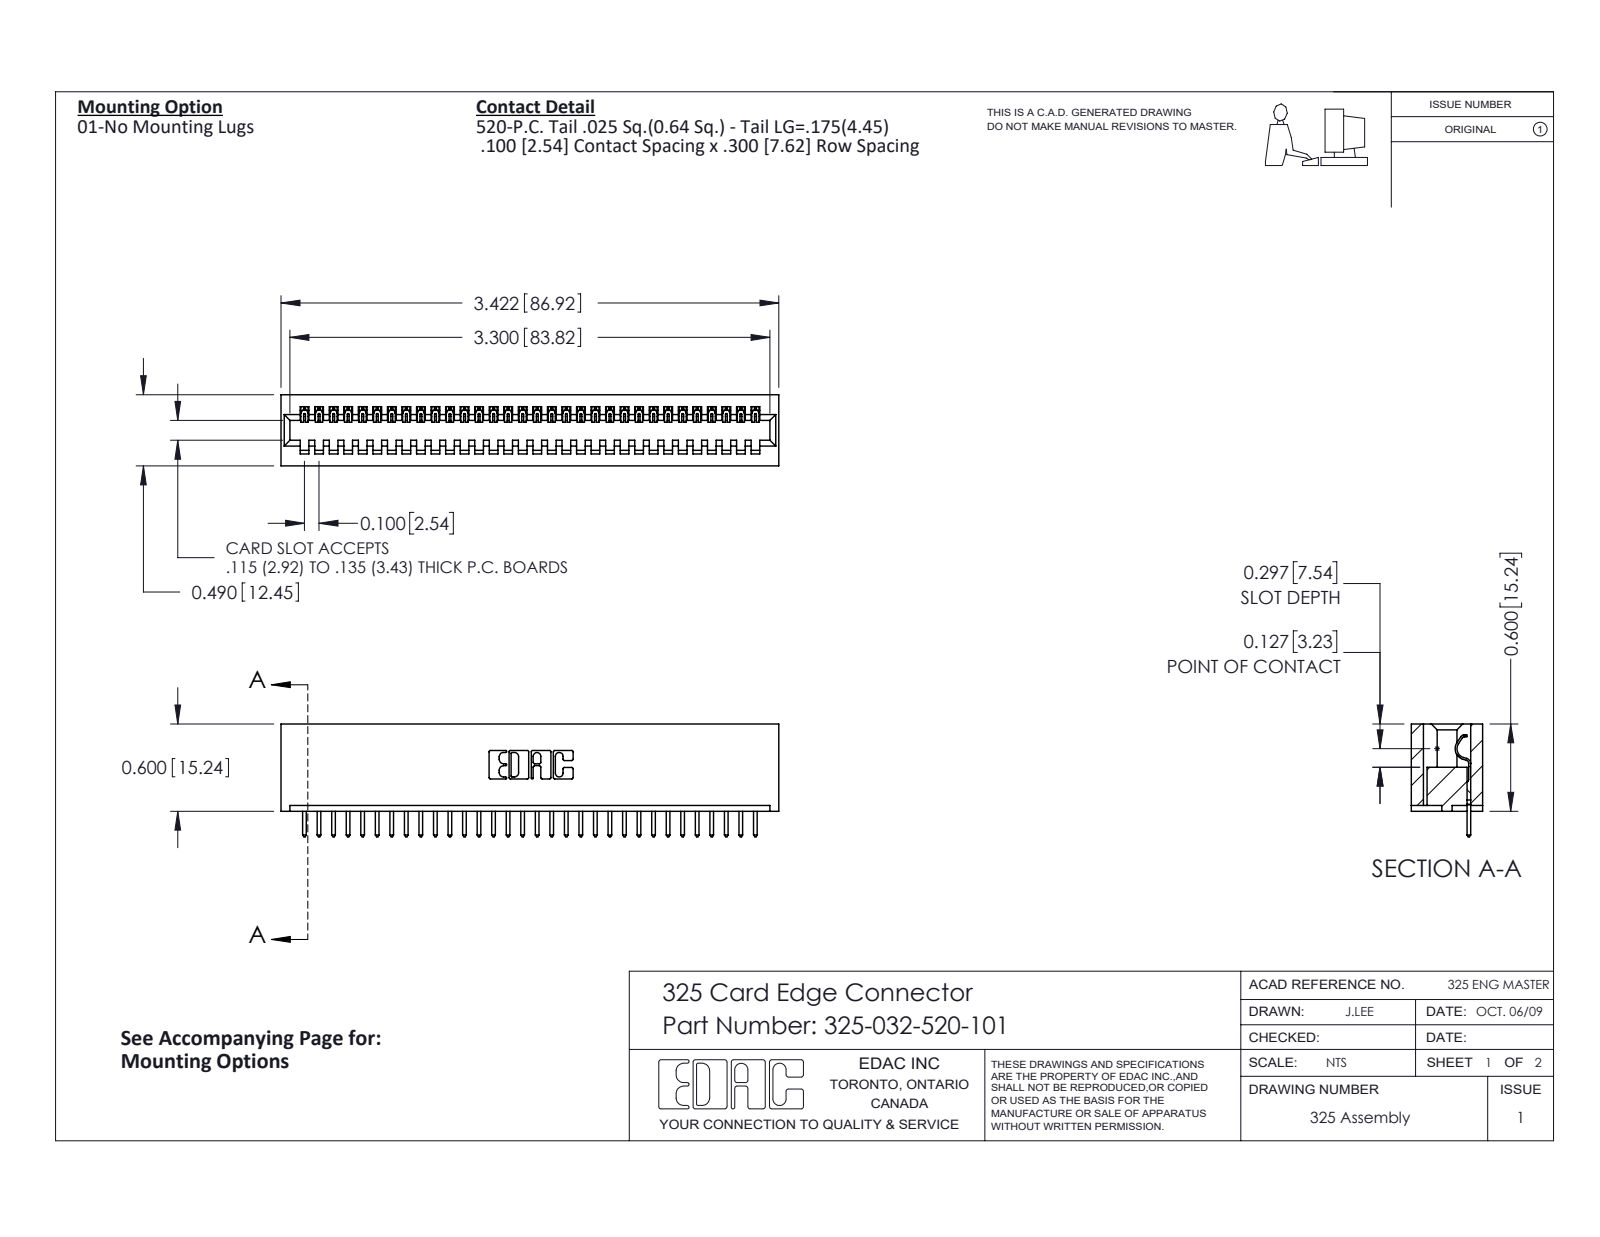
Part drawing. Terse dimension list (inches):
name: 325 Part_Lugless; 325-032-520-101; 325-292-001_325-293-120
written by: SolidWorks 2016 (CONFIG_CONTROL_DESIGN)
unit: in
bodies: 33 solids, 1962 faces (1410 planar, 552 cylindrical, 0 other)
size: 3.422 × 0.775 × 0.49
volume: 0.698 in³; area: 19.36 in²
rounds: 64× R0.006, 64× R0.01, 22× R0.01, 6× R0.007, 6× R0.031, 3× R0.026, 1× R0.014, 1× R0.022
face distances: 0.083, 0.407, 0.3, 0.49, 0.107, 0.383, 0.025, 0.325, 0.1, 0.2
